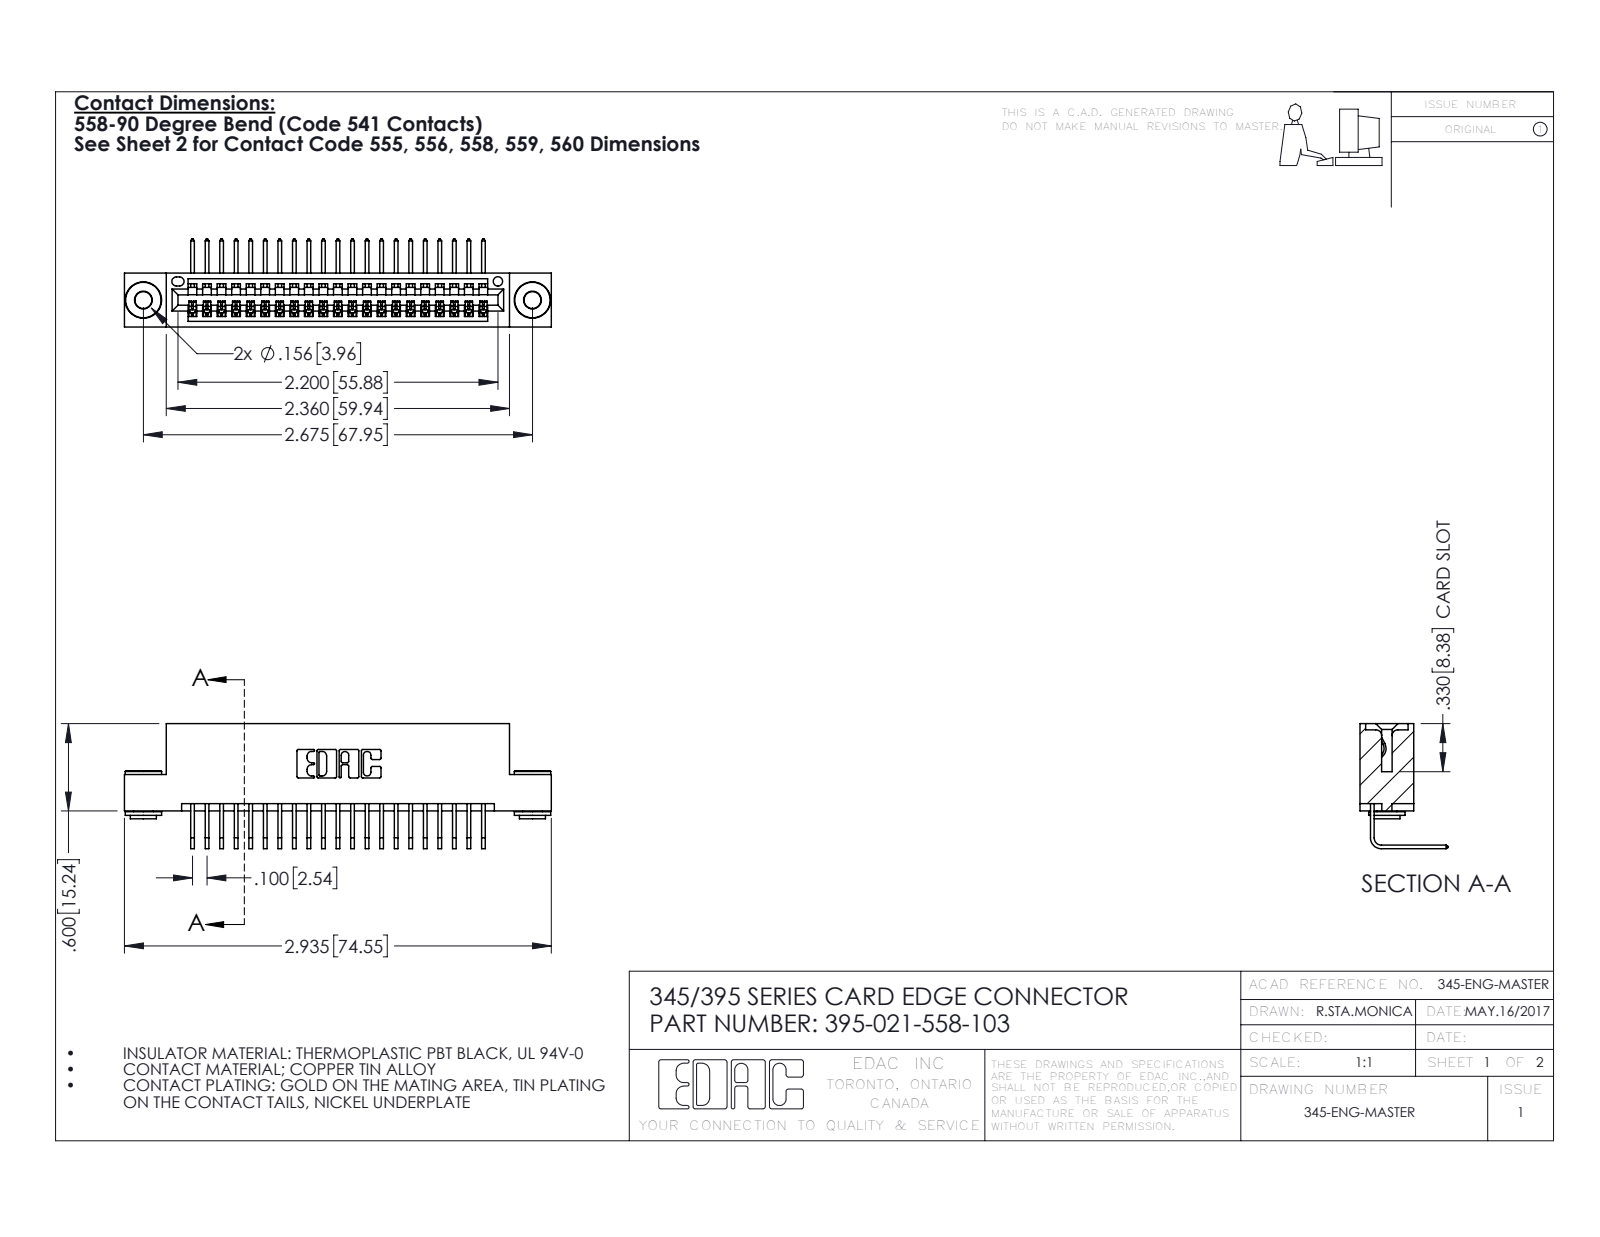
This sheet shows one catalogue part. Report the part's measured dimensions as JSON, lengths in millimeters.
{"part_name": "345-250-002_345-250-002-102; 345-292-001_558 Tail - 2; 345 Part_Flush Mounting Lugs - 0.156 Dia-TH; 395-021-558-103", "step_written_by": "SolidWorks 2016 (CONFIG_CONTROL_DESIGN)", "units": "millimeters", "bodies": {"solids": 24, "faces": 1424, "planar": 972, "cylindrical": 444, "other": 8}, "overall_size": [74.5, 21.8, 15.4], "volume_mm3": 7000, "surface_area_mm2": 9639, "round_holes": [[2.9, 2], [4, 2], [1.6, 1]], "round_bosses_or_shafts": [[6.4, 2], [4.6, 2], [3.5, 2]], "partial_cylinders_radius": [[0.2, 42], [0.3, 22], [0.2, 6], [0.8, 6], [0.7, 3], [0.8, 2], [1, 2], [0.4, 1]], "face_to_face_distances": [1.8, 7.6, 5.1, 9.4, 0.6, 2.5, 6.9, 5.7, 3.8, 1.8], "hole_center_spacings": [6.9, 62, 67.9]}
